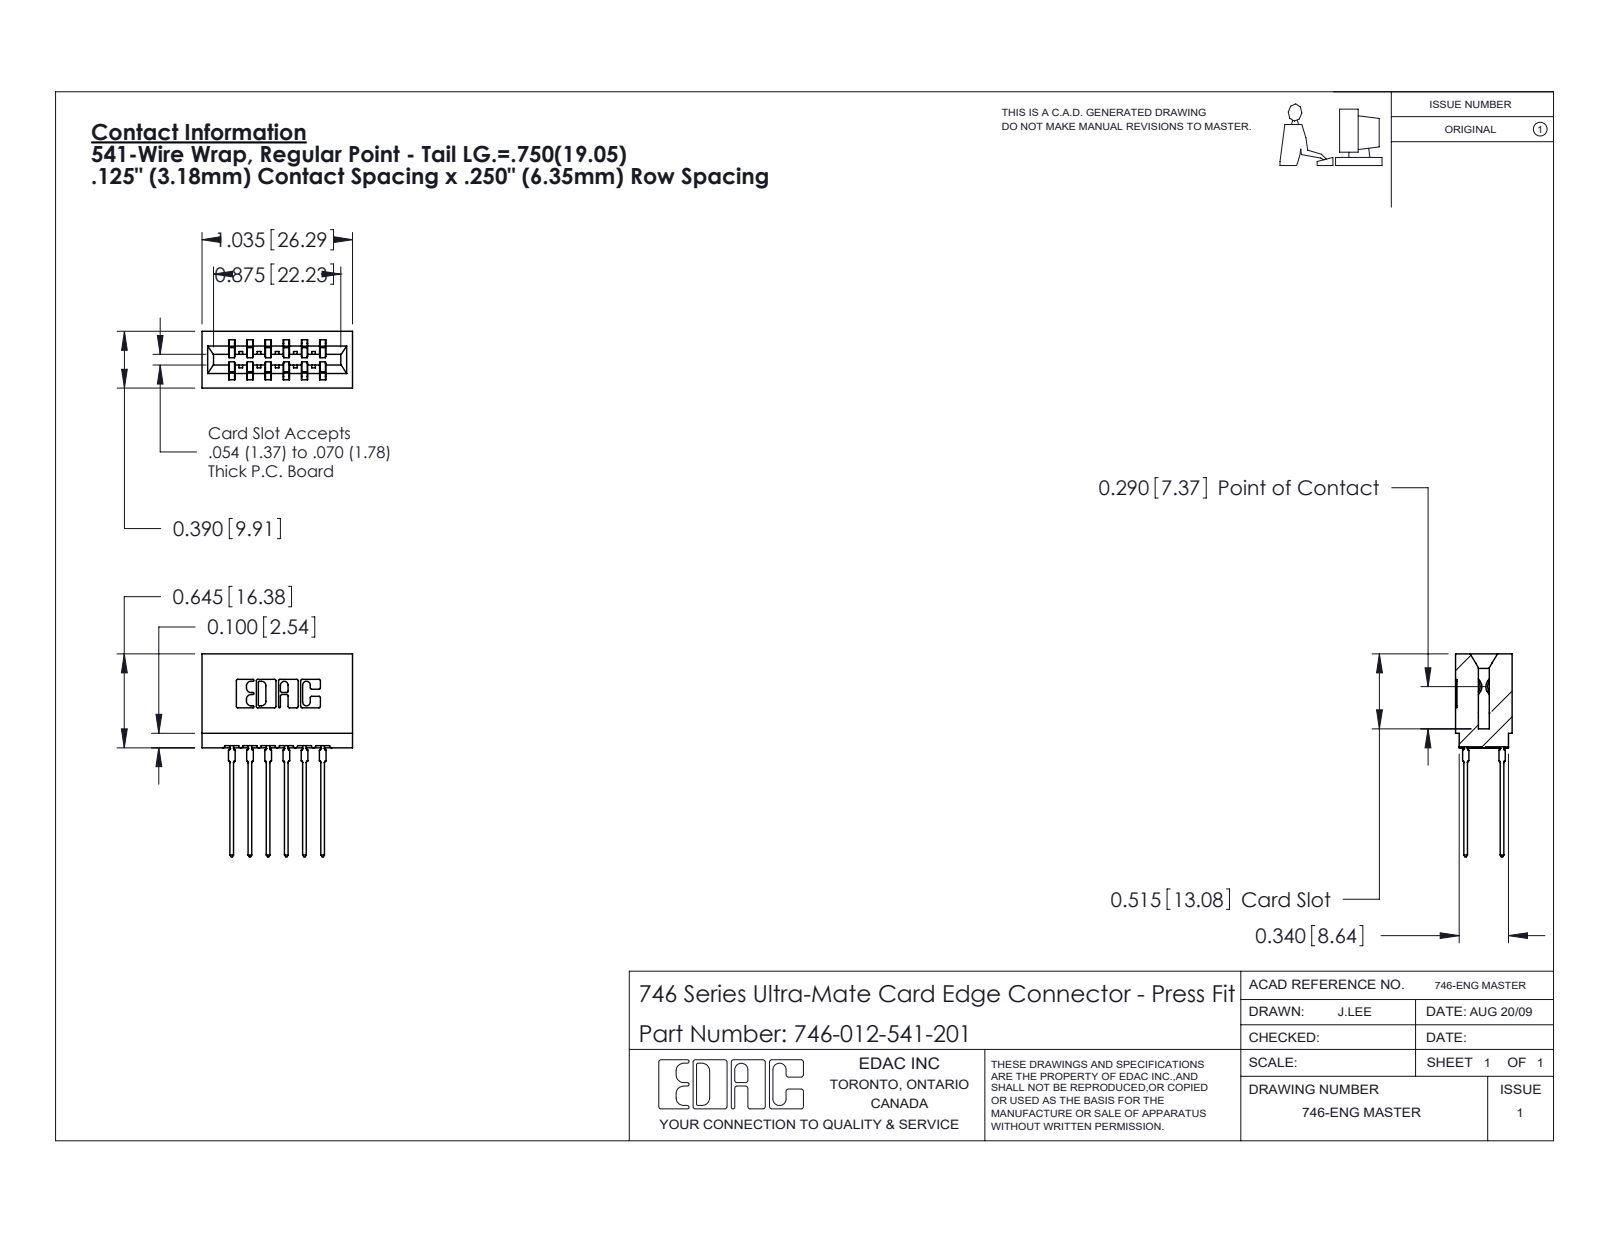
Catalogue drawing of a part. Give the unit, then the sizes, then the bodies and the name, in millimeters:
Units: millimetres
Overall size (bounding box): 35.4 × 26.3 × 9.9
Partial cylindrical surfaces — rounded edges, fillets, slot ends (radius × count): R0.5 ×24, R0.3 ×22, R0.1 ×8, R0.3 ×8, R0.4 ×7, R0.2 ×6, R0.8 ×6, R0.7 ×3
Main face-to-face distances: 6.4, 1.4, 8.5, 3.2, 1.1, 2.1, 0.6, 9.5, 7.8, 3.2
Volume: 3 110 mm³ · Surface area: 4 588 mm²
Bodies: 13 solids, 1171 faces (607 planar, 252 cylindrical, 312 other)
Part name (STEP PRODUCT): 746-012-541-201; 746 Part_.515 Slot Depth - 01; 746-292-001_541
STEP written by: SolidWorks 2020 (CONFIG_CONTROL_DESIGN)
